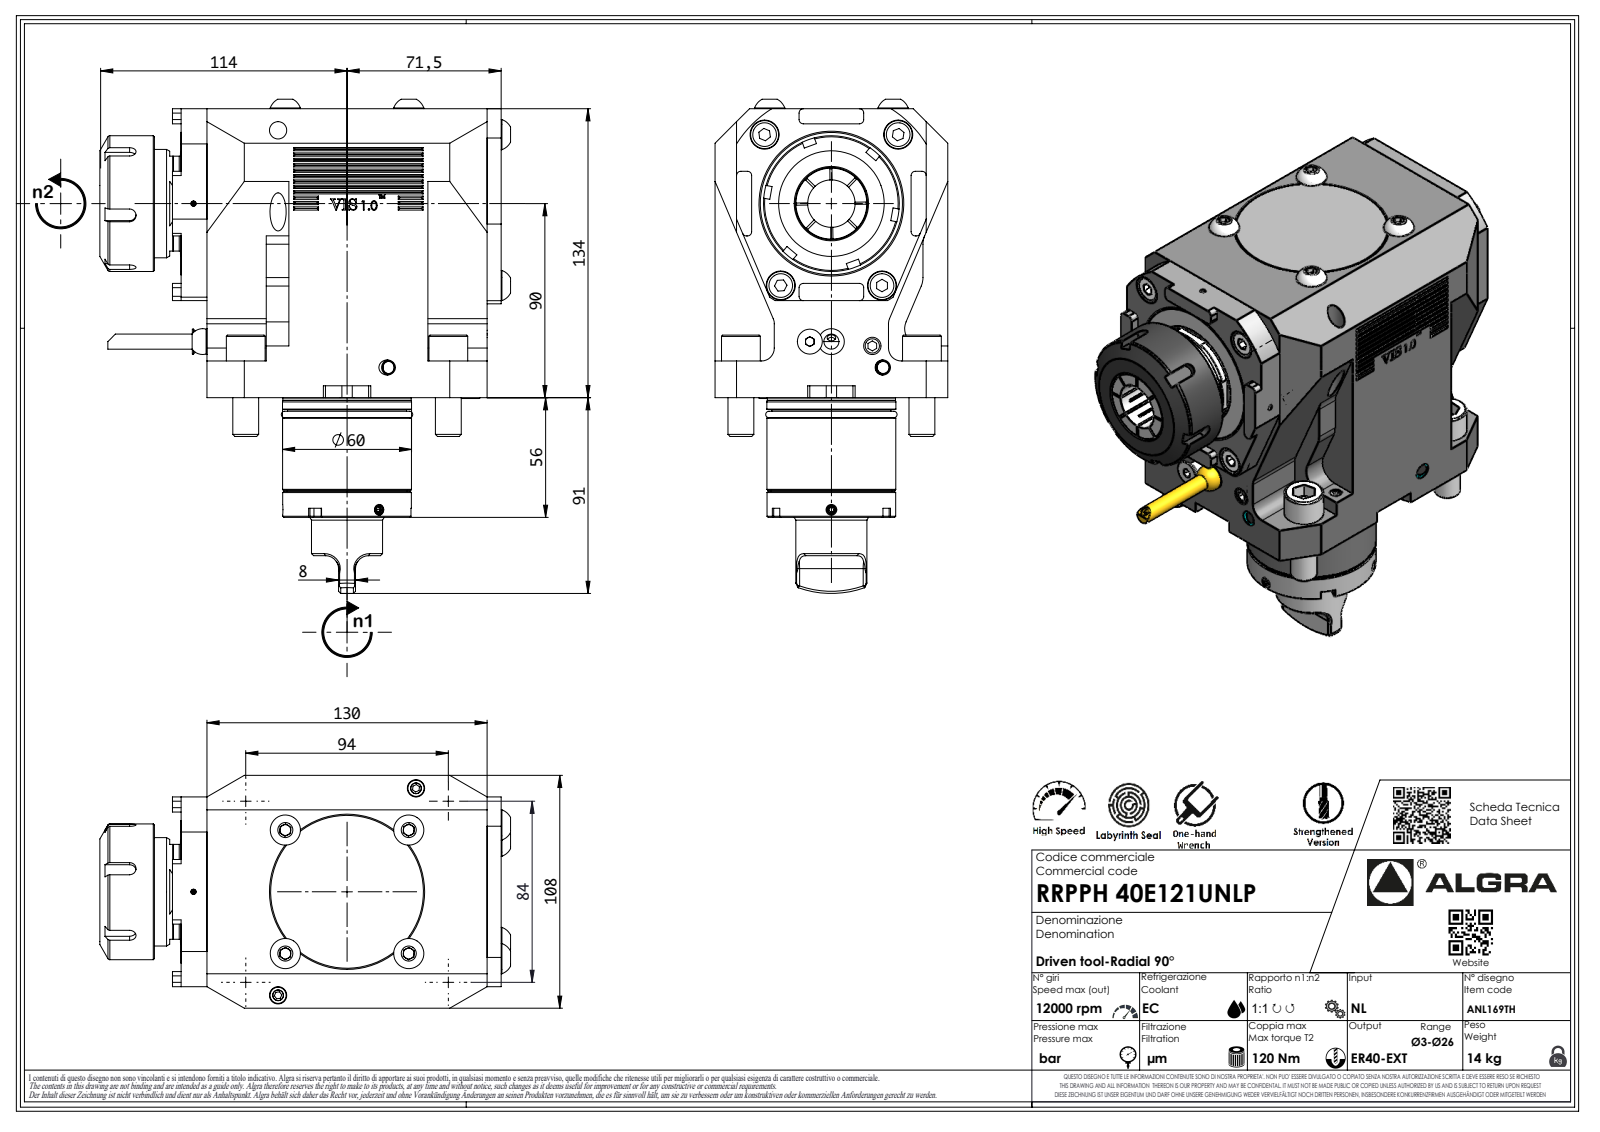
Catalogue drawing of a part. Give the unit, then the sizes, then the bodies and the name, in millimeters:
Units: millimetres
Overall size (bounding box): 224.8 × 186.2 × 108
Round holes (diameter × count): ⌀2.1 ×1, ⌀4 ×1
Round bosses / shafts (diameter × count): ⌀18 ×4, ⌀12 ×4, ⌀63 ×1, ⌀59.9 ×1, ⌀59.8 ×1, ⌀59.7 ×1, ⌀59.5 ×1, ⌀55.2 ×1
Partial cylindrical surfaces — rounded edges, fillets, slot ends (radius × count): R0.2 ×21, R8 ×18, R2 ×16, R6 ×10, R3 ×9, R0.33 ×7, R0.52 ×7, R3.7 ×7
Main face-to-face distances: 108, 134, 27.5, 12, 102.5, 6.5, 136.5, 5.5, 148.5, 39.5
Volume: 2 078 000 mm³ · Surface area: 132 307 mm²
Bodies: 1 solid, 1009 faces (686 planar, 139 cylindrical, 184 other)
Part name (STEP PRODUCT): RRPPH40E121UNLP
STEP written by: SolidWorks 2023 (AUTOMOTIVE_DESIGN)
